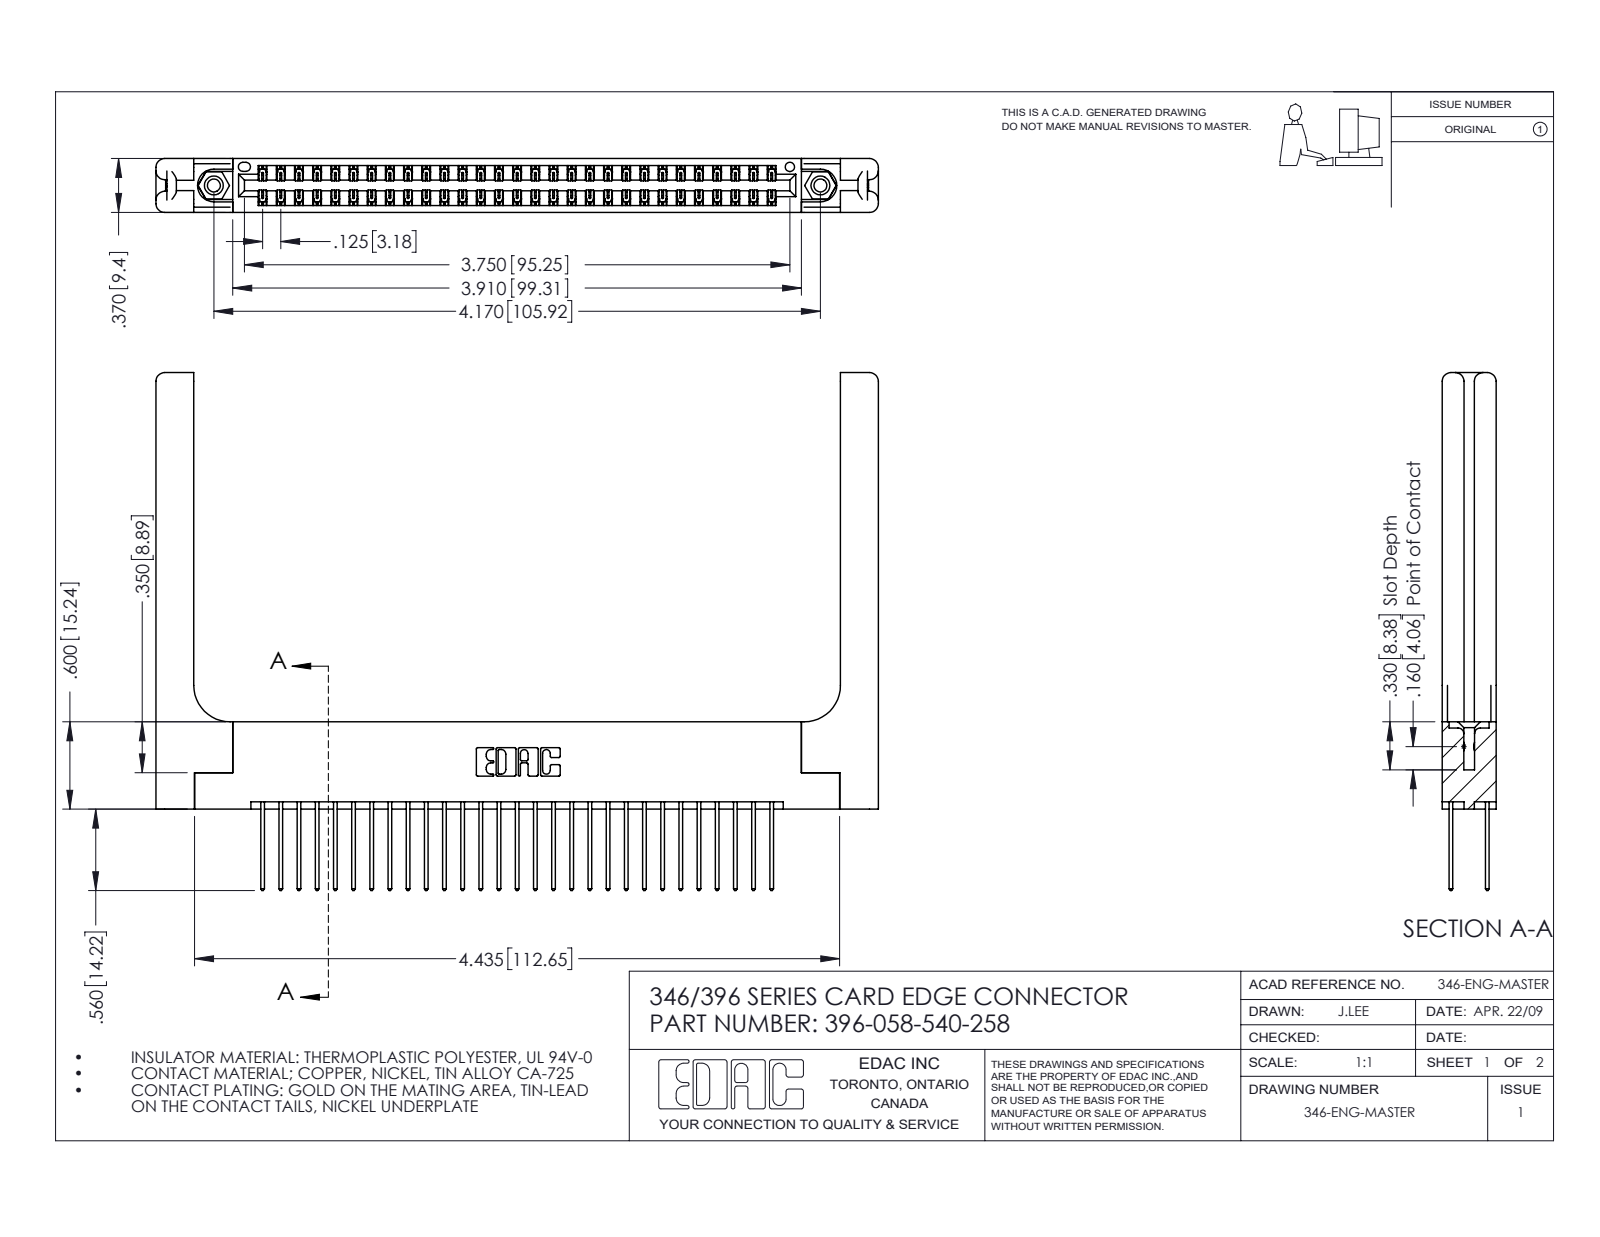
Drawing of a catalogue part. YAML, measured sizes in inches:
part_name: "345-250-001_345-250-001-102; 346 Part_Flush Mounting Lugs - 0.156 Dia-TH; 396-058-540-258; 346-220-058_345-220-058 (+1 more)"
step_written_by: "SolidWorks 2016 (CONFIG_CONTROL_DESIGN)"
units: inches
bodies: {solids: 63, faces: 3394, planar: 2254, cylindrical: 1080, other: 60}
overall_size: [4.966, 3.56, 0.37]
volume: 1.215
surface_area: 35.46
round_holes:
  - {diameter: 0.089, count: 2}
  - {diameter: 0.125, count: 2}
  - {diameter: 0.156, count: 2}
  - {diameter: 0.064, count: 1}
round_bosses_or_shafts:
  - {diameter: 0.155, count: 2}
partial_cylinders:
  - {radius: 0.006, count: 87}
  - {radius: 0.01, count: 58}
  - {radius: 0.01, count: 22}
  - {radius: 0.06, count: 16}
  - {radius: 0.007, count: 6}
  - {radius: 0.031, count: 6}
  - {radius: 0.026, count: 3}
  - {radius: 0.014, count: 2}
face_to_face_distances: [0.048, 0.322, 0.37, 0.072, 0.25, 0.025, 0.298, 0.15, 0.148, 0.275]
hole_center_spacings: [0.246, 3.962, 4.17]
